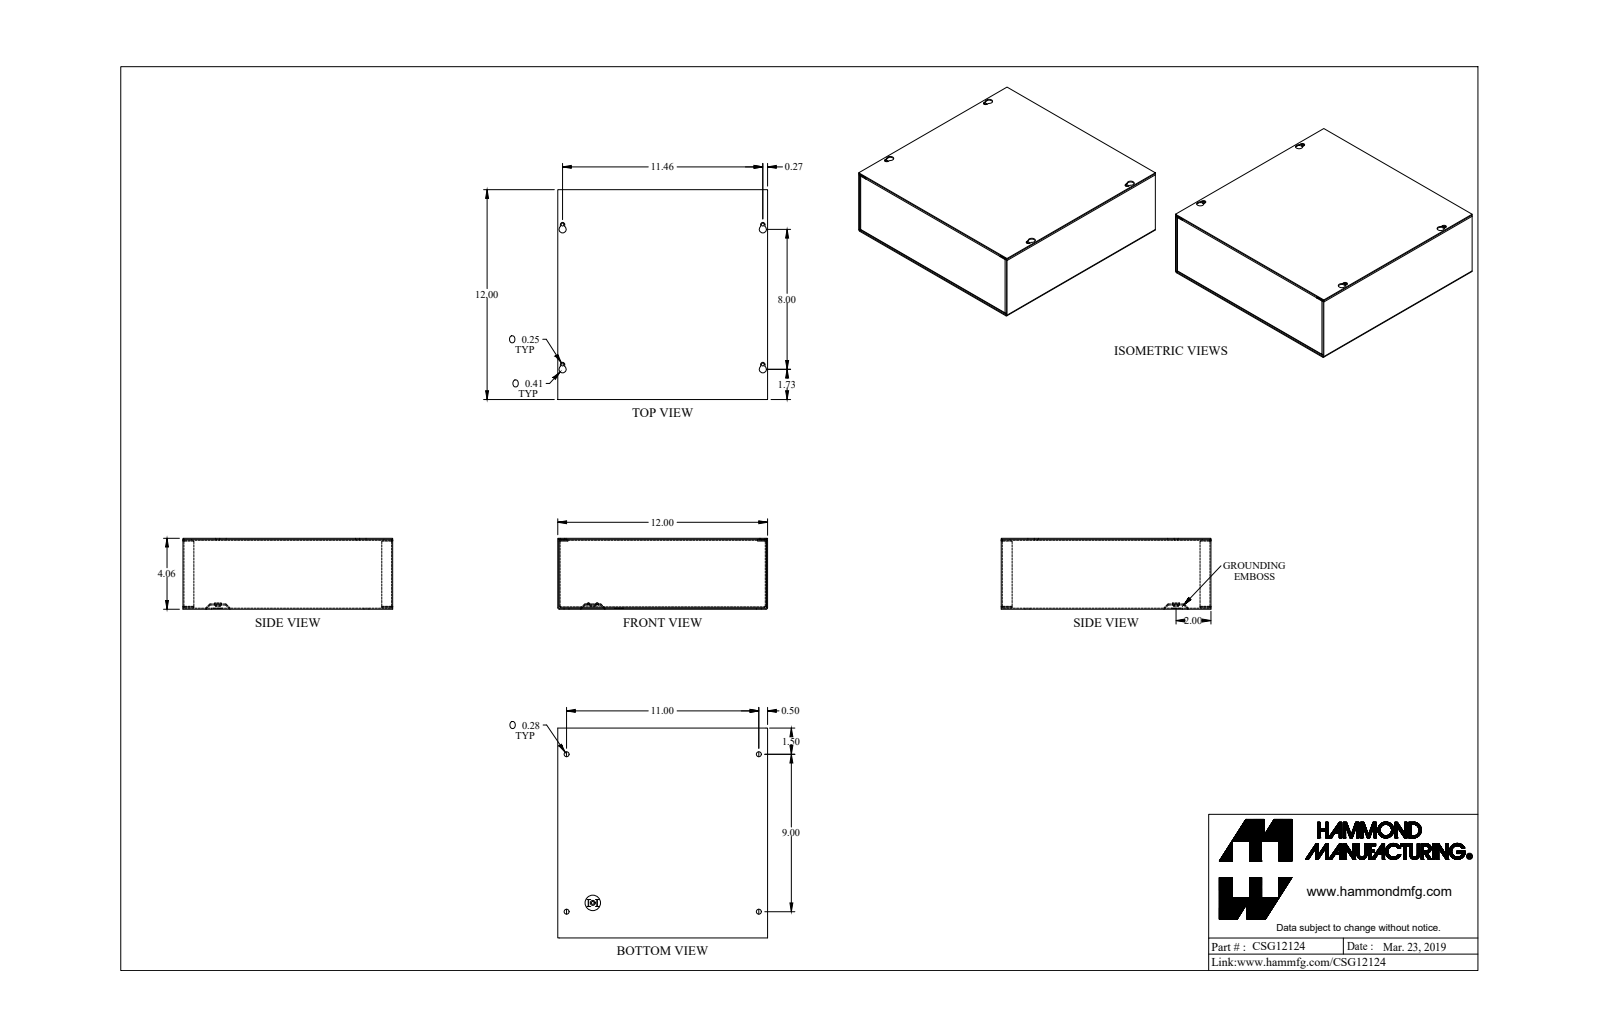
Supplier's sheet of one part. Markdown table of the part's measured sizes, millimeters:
| quantity | value |
| --- | --- |
| part name | CSG12124_Default |
| STEP written by | SolidWorks 2019 (CONFIG_CONTROL_DESIGN) |
| units | millimeters |
| bodies | 4 solids, 205 faces (125 planar, 72 cylindrical, 8 other) |
| overall size | 304.8 × 304.8 × 103 |
| volume | 480 300 mm³ |
| surface area | 671 000 mm² |
| round holes (diameter × count) | 4.3 × 5, 7.1 × 4, 12.7 × 1 |
| round bosses / shafts (diameter × count) | 12.5 × 1, 7.2 × 1 |
| partial cylindrical surfaces (radius × count) | 0.7 × 12, 2.2 × 12, 1.4 × 8, 3.2 × 4, 5.2 × 4 |
| main face-to-face distances | 1.4, 101.6, 303.4, 100.2, 103, 304.8, 301.9, 2, 98.1, 99.6 |
| hole center spacings | 14, 216, 285.5, 357.7, 203.2, 228.6, 279.4, 291.1 |
